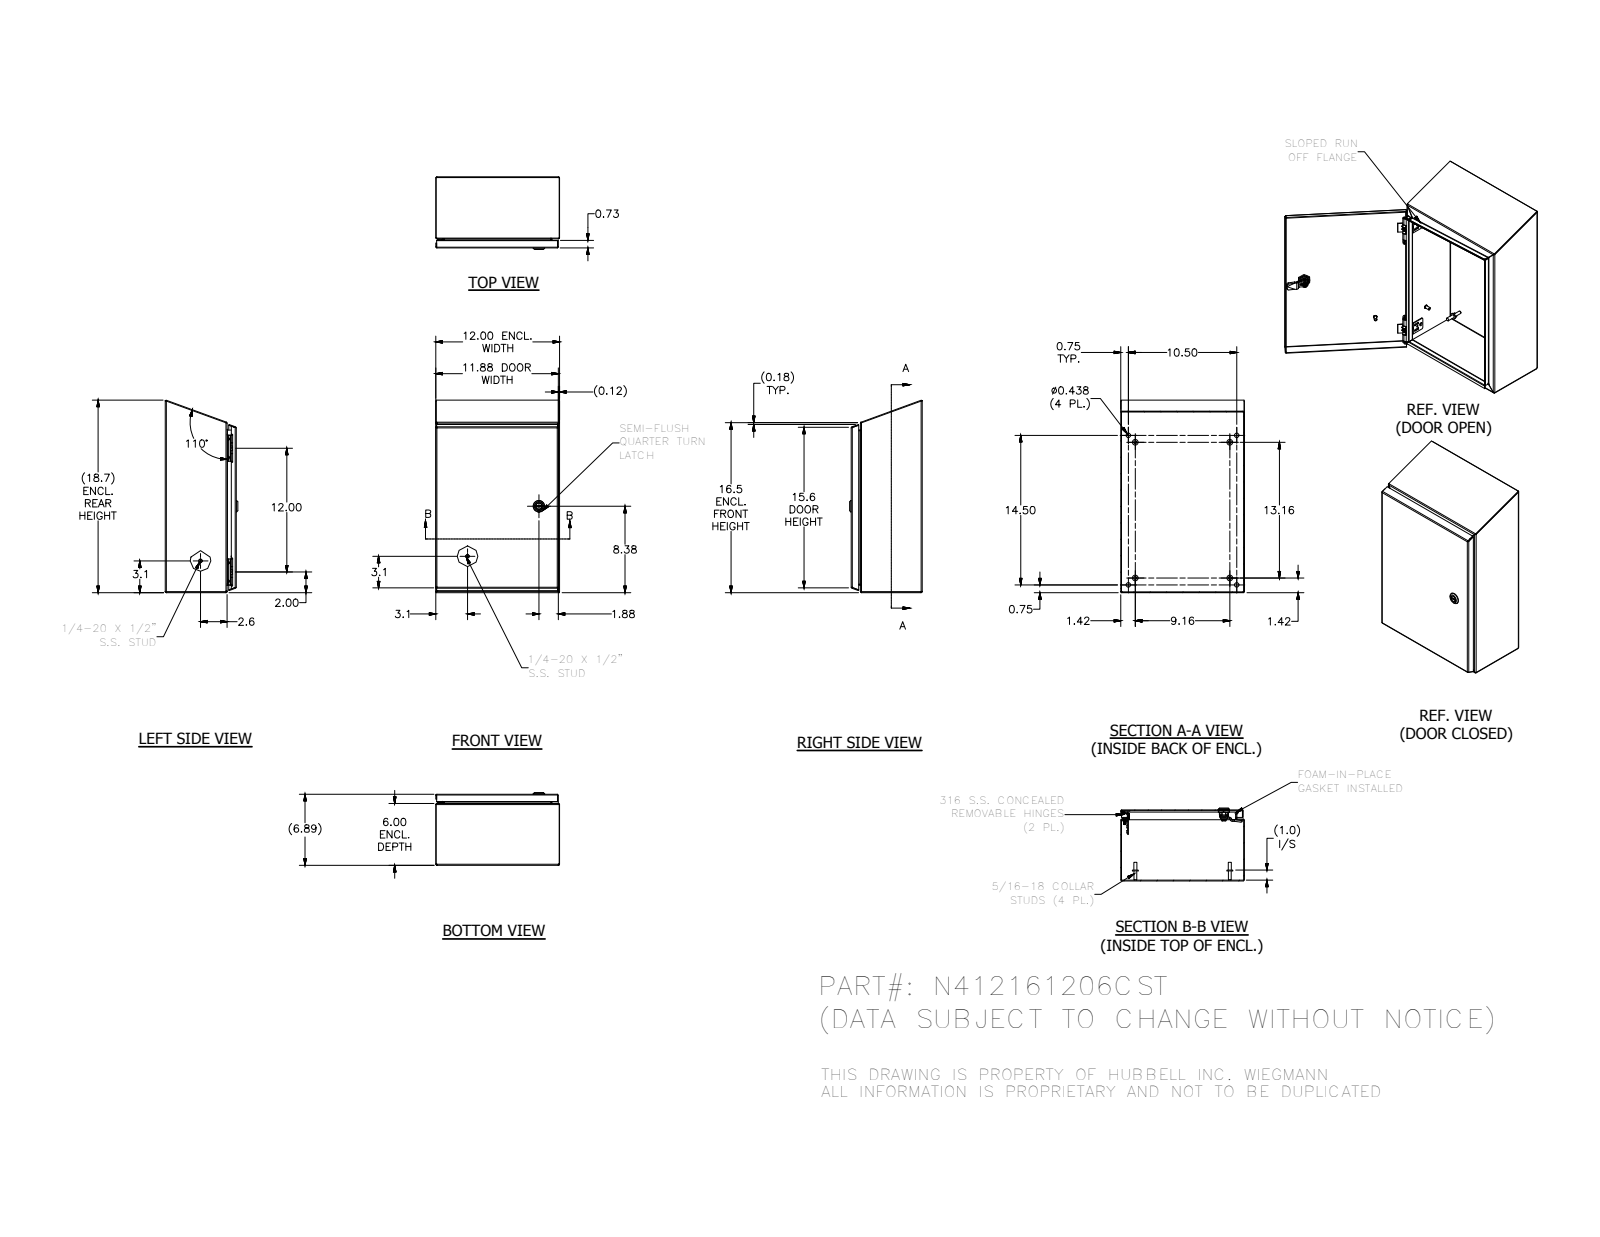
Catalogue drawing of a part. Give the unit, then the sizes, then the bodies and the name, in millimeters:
Units: millimetres
Overall size (bounding box): 474 × 304.8 × 178.9
Round holes (diameter × count): ⌀2.4 ×4, ⌀3.9 ×4, ⌀4.2 ×4, ⌀4.4 ×4, ⌀4.7 ×4, ⌀11.1 ×4, ⌀4 ×3, ⌀4.7 ×1, ⌀5 ×1, ⌀8 ×1, ⌀10 ×1, ⌀10.2 ×1
Round bosses / shafts (diameter × count): ⌀6.4 ×10, ⌀14.3 ×4, ⌀9.1 ×4, ⌀8.1 ×4, ⌀7.6 ×4, ⌀7 ×4, ⌀6.5 ×4, ⌀4.2 ×4
Partial cylindrical surfaces — rounded edges, fillets, slot ends (radius × count): R0.3 ×30, R0.8 ×29, R1.3 ×26, R2.7 ×19, R0.4 ×18, R3.2 ×16, R0.5 ×13, R0.8 ×8
Main face-to-face distances: 1.9, 173.1, 302.9, 171.2, 174.9, 304.8, 301, 150.5, 22.5, 1.9
Hole centre spacings: 304.8, 12.7, 16.7, 16.8, 33.2, 33.3, 49.9, 266.7
Volume: 1 097 000 mm³ · Surface area: 1 176 000 mm²
Bodies: 36 solids, 1520 faces (567 planar, 552 cylindrical, 401 other)
Part name (STEP PRODUCT): N412161206CST
STEP written by: SolidWorks 2018 (AUTOMOTIVE_DESIGN)
